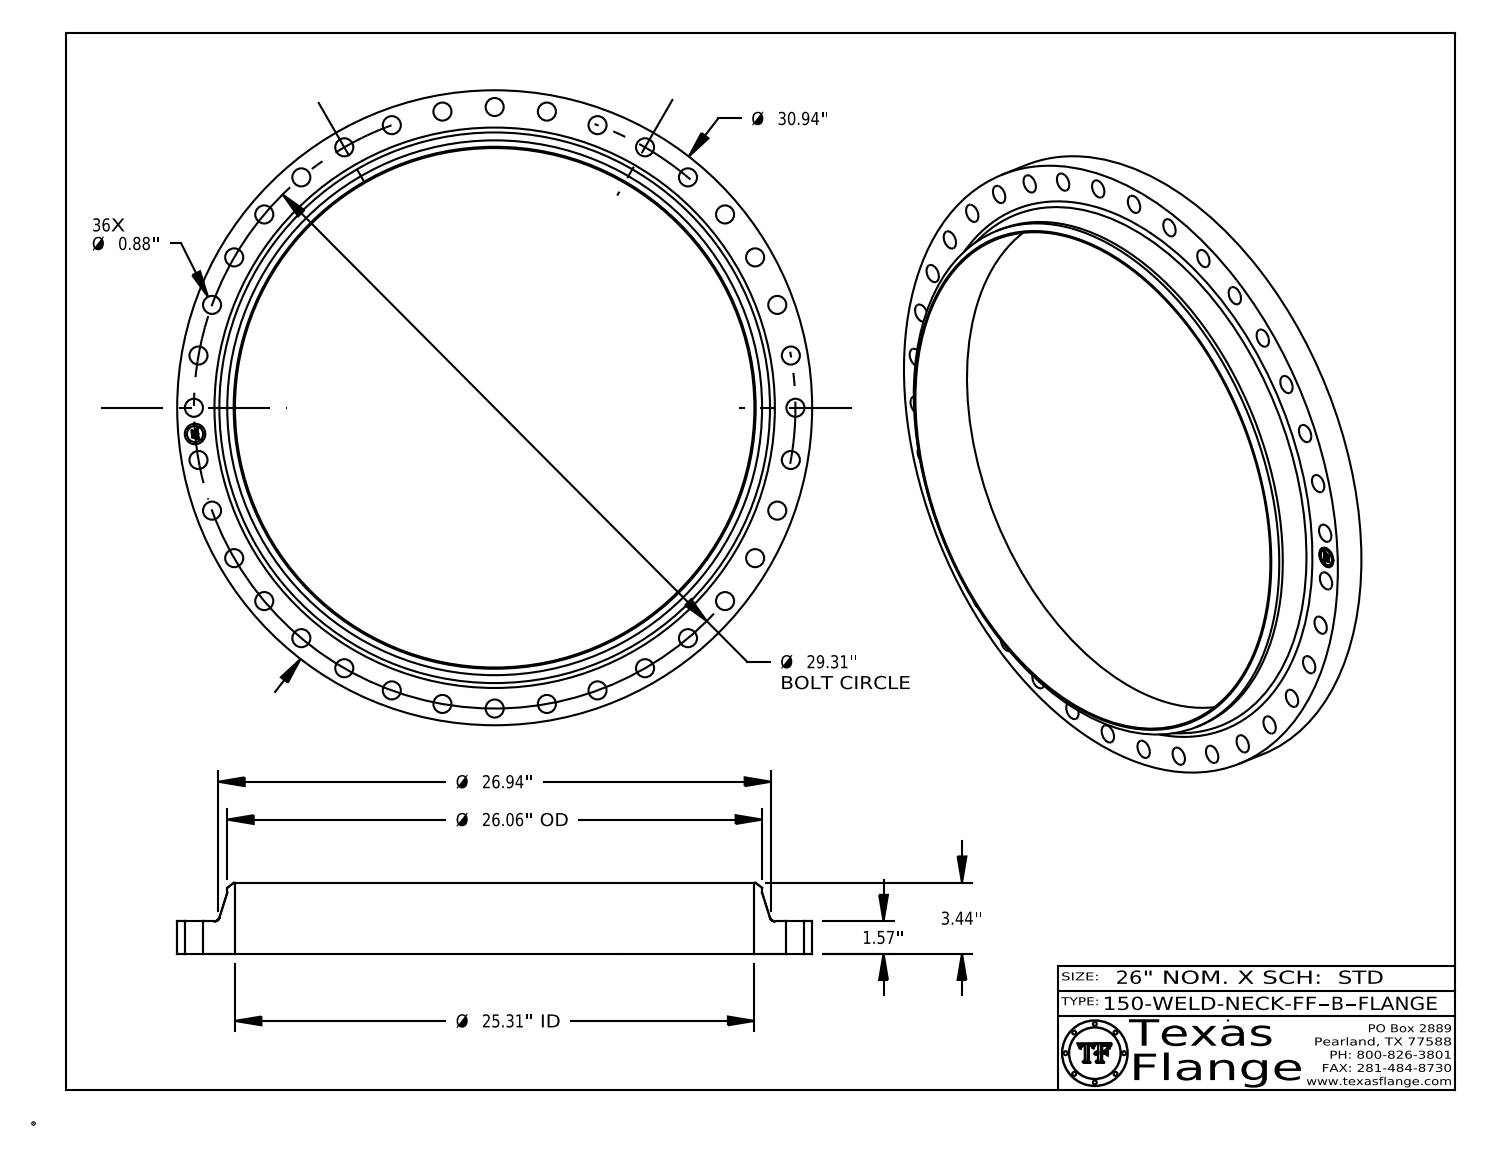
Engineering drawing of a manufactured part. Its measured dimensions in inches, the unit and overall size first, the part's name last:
Units: inches
Overall size (bounding box): 30.94 × 30.94 × 3.44
Round holes (diameter × count): ⌀0.88 ×36, ⌀1 ×1, ⌀25.31 ×1
Round bosses / shafts (diameter × count): ⌀0.061 ×8, ⌀30.94 ×1, ⌀26.06 ×1, ⌀0.788 ×1
Main face-to-face distances: 1.57, 3.44, 1.87, 1.555, 0.015, 1.885, 0.298, 0.293, 0.054, 0.193
Hole centre spacings: 14.655, 28.311, 12.387, 18.84, 24.009, 27.543, 29.198, 2.555
Volume: 435.6 in³ · Surface area: 1 143 in²
Bodies: 1 solid, 472 faces (368 planar, 98 cylindrical, 6 other)
Part name (STEP PRODUCT): 150-WELD-NECK-FF, Series B
STEP written by: CATIA V5 STEP AP214 (AUTOMOTIVE_DESIGN)
